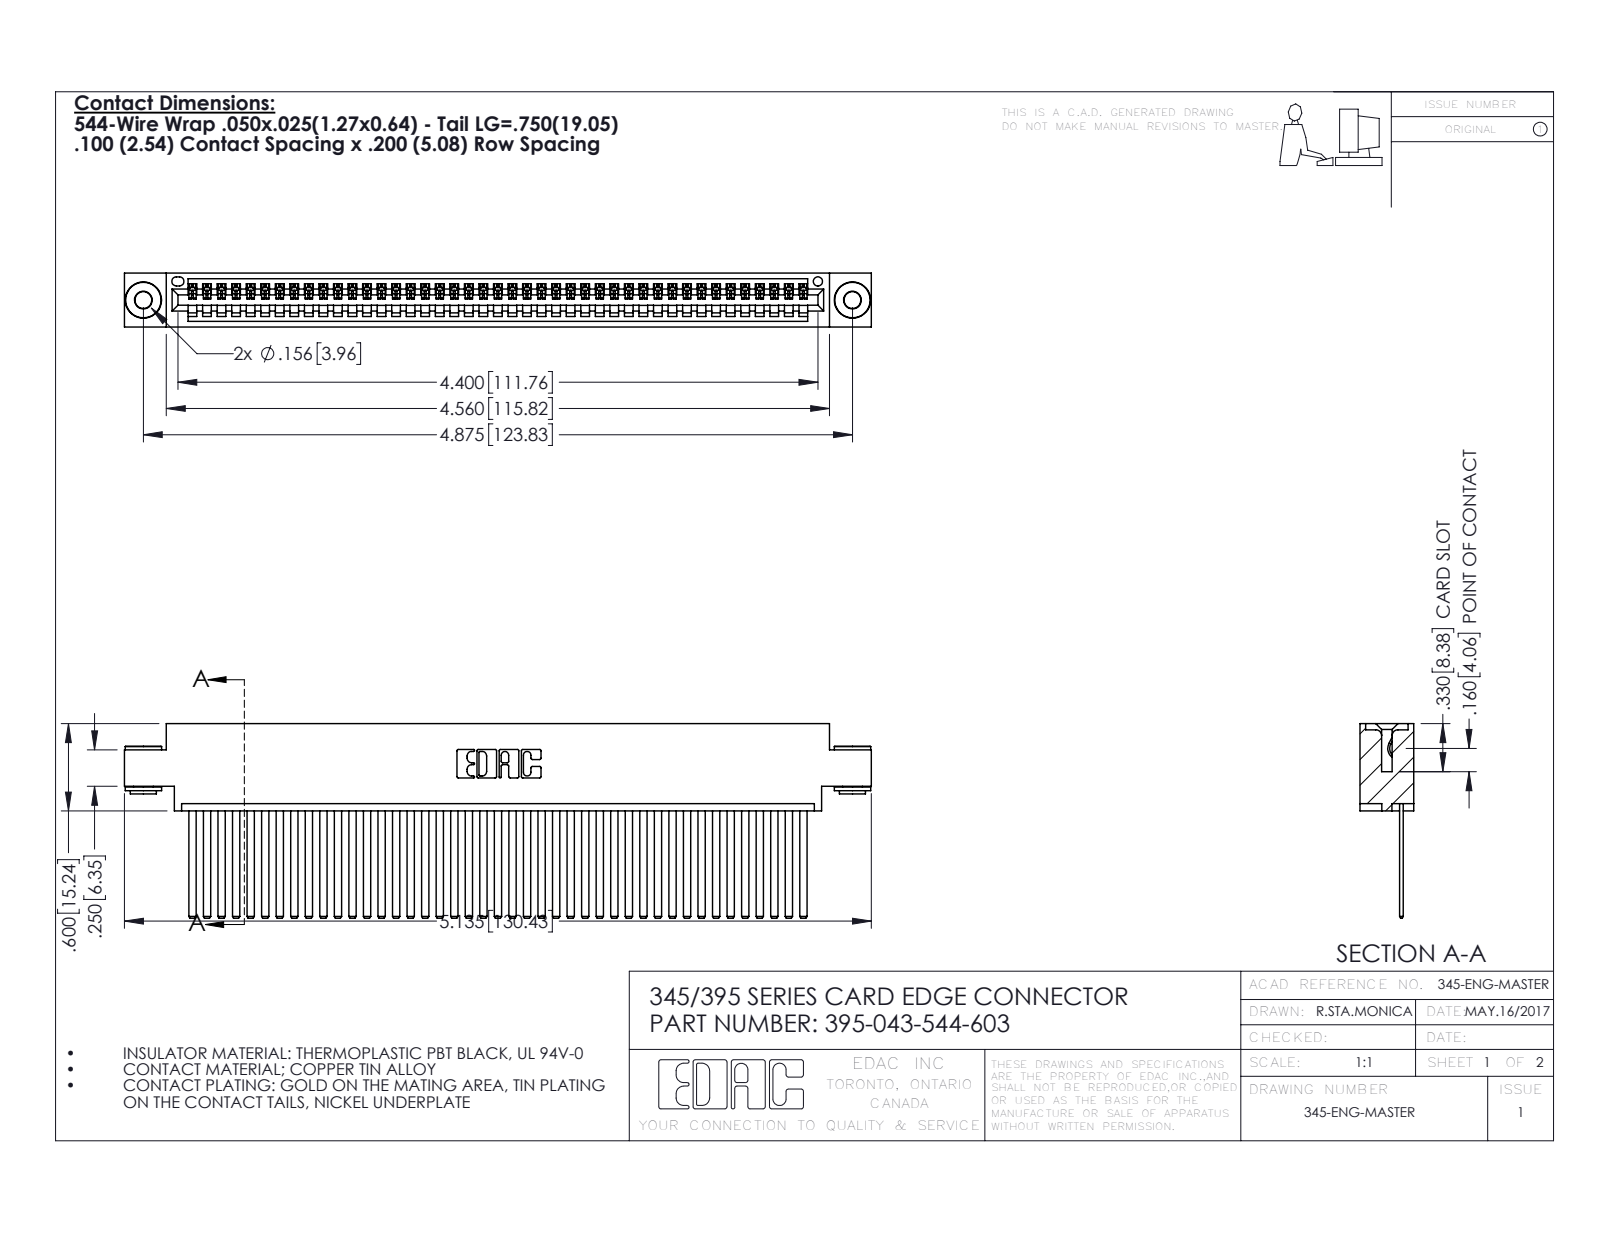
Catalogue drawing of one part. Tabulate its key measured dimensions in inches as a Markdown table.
| quantity | value |
| --- | --- |
| part name | 345-292-001_345-293-144; 395-043-544-603; 345 Part_0.170 Offset - 0.156 Dia-TH; 345-250-002_345-250-002-102 |
| STEP written by | SolidWorks 2016 (CONFIG_CONTROL_DESIGN) |
| units | inches |
| bodies | 46 solids, 2404 faces (1642 planar, 754 cylindrical, 8 other) |
| overall size | 5.135 × 1.337 × 0.37 |
| volume | 0.781 in³ |
| surface area | 29.23 in² |
| round holes (diameter × count) | 0.116 × 2, 0.156 × 2, 0.064 × 1 |
| round bosses / shafts (diameter × count) | 0.25 × 2, 0.18 × 2, 0.136 × 2 |
| partial cylindrical surfaces (radius × count) | 0.006 × 86, 0.01 × 22, 0.007 × 6, 0.031 × 6, 0.026 × 3, 0.031 × 2, 0.04 × 2, 0.014 × 1 |
| main face-to-face distances | 0.072, 0.298, 0.025, 0.098, 0.272, 0.37, 0.2, 0.225, 0.175, 0.149 |
| hole center spacings | 0.27, 4.639, 4.875 |
